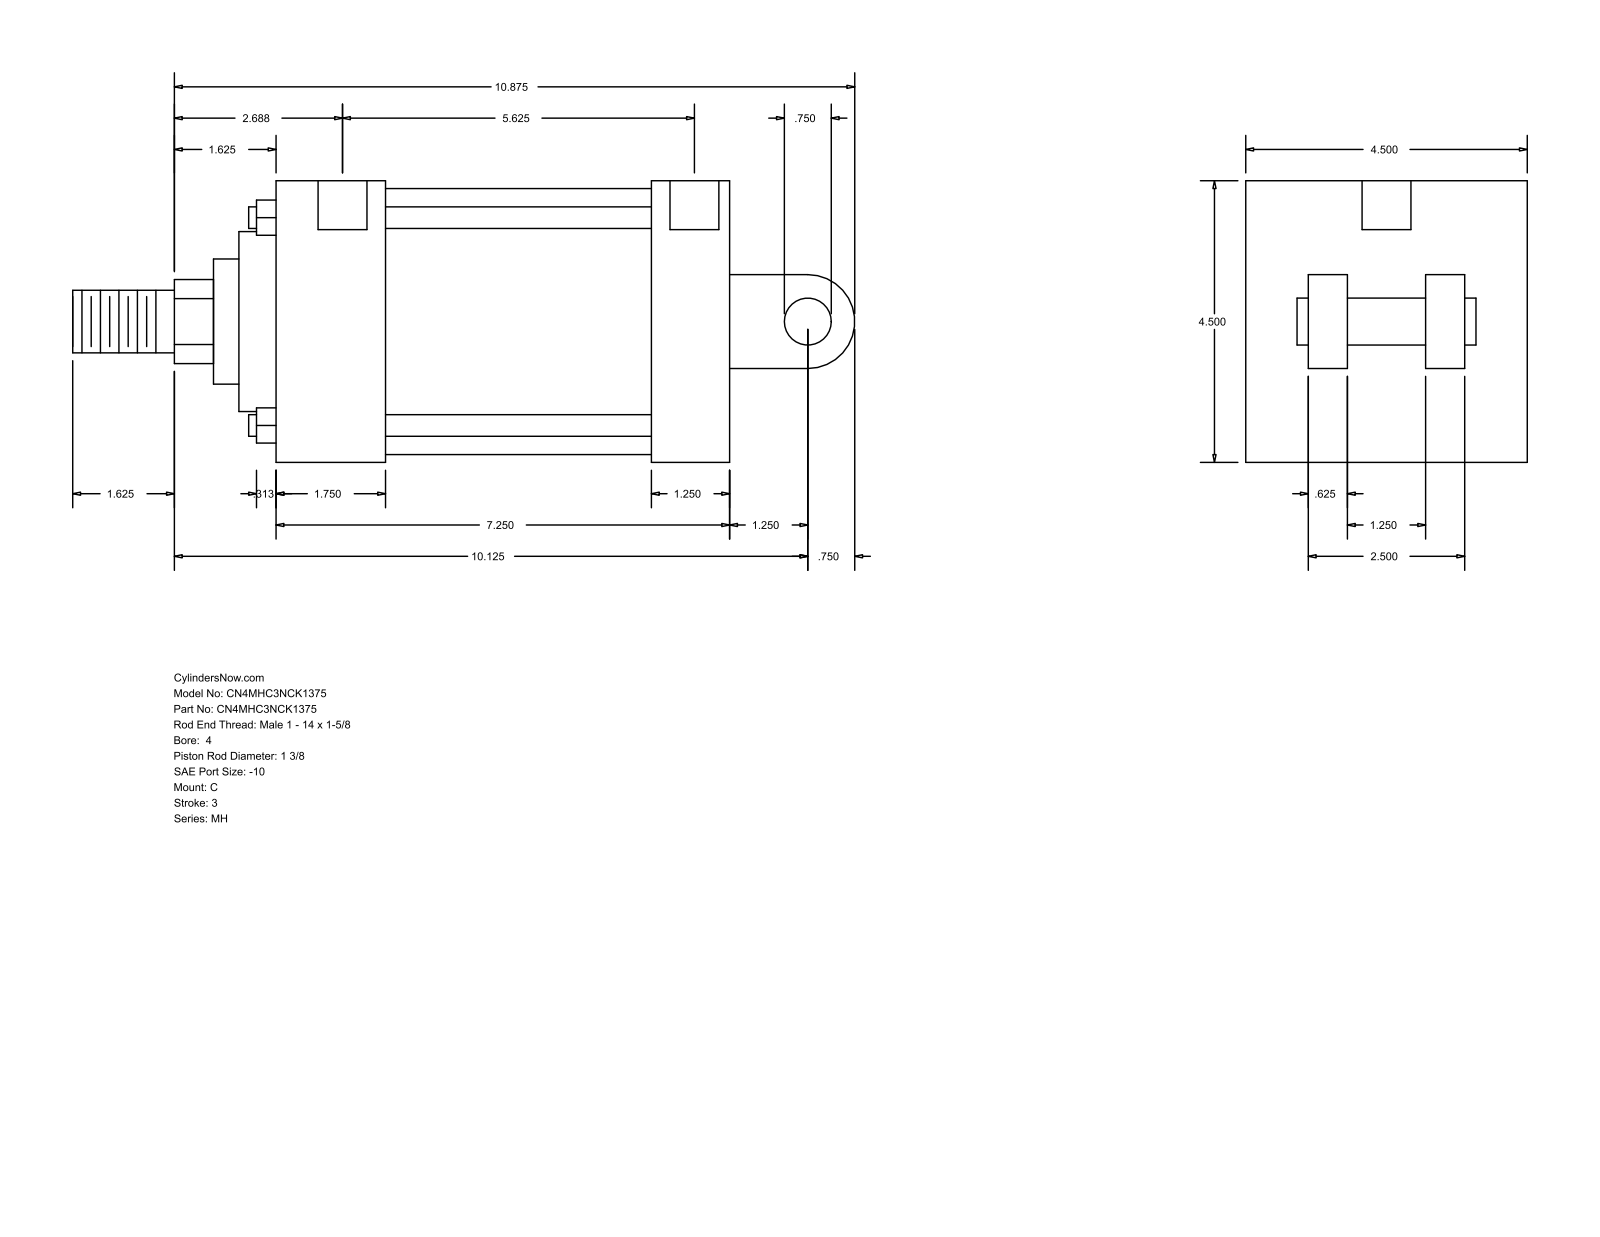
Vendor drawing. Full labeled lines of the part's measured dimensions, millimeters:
Part name (STEP PRODUCT): MH_C__0400_1.375
STEP written by: GSSL Pune (CONFIG_CONTROL_DESIGN)
Units: millimetres
Bodies: 0 solids, 101 faces (71 planar, 30 cylindrical, 0 other)
Overall size (bounding box): 317.5 × 114.3 × 114.3
Round holes (diameter × count): ⌀8.73 ×4, ⌀19.84 ×2
Round bosses / shafts (diameter × count): ⌀8.76 ×4, ⌀107.95 ×1, ⌀73.03 ×1, ⌀50.8 ×1, ⌀34.92 ×1, ⌀25.4 ×1, ⌀19.05 ×1
Partial cylindrical surfaces — rounded edges, fillets, slot ends (radius × count): R17.06 ×1, R19.05 ×1
Main face-to-face distances: 114.3, 184.16, 44.45, 152.41, 107.96, 139.71, 31.75, 41.27, 73.03, 38.1
Hole centre spacings: 146.05, 1.58, 1.59, 142.88, 144.46, 144.47
